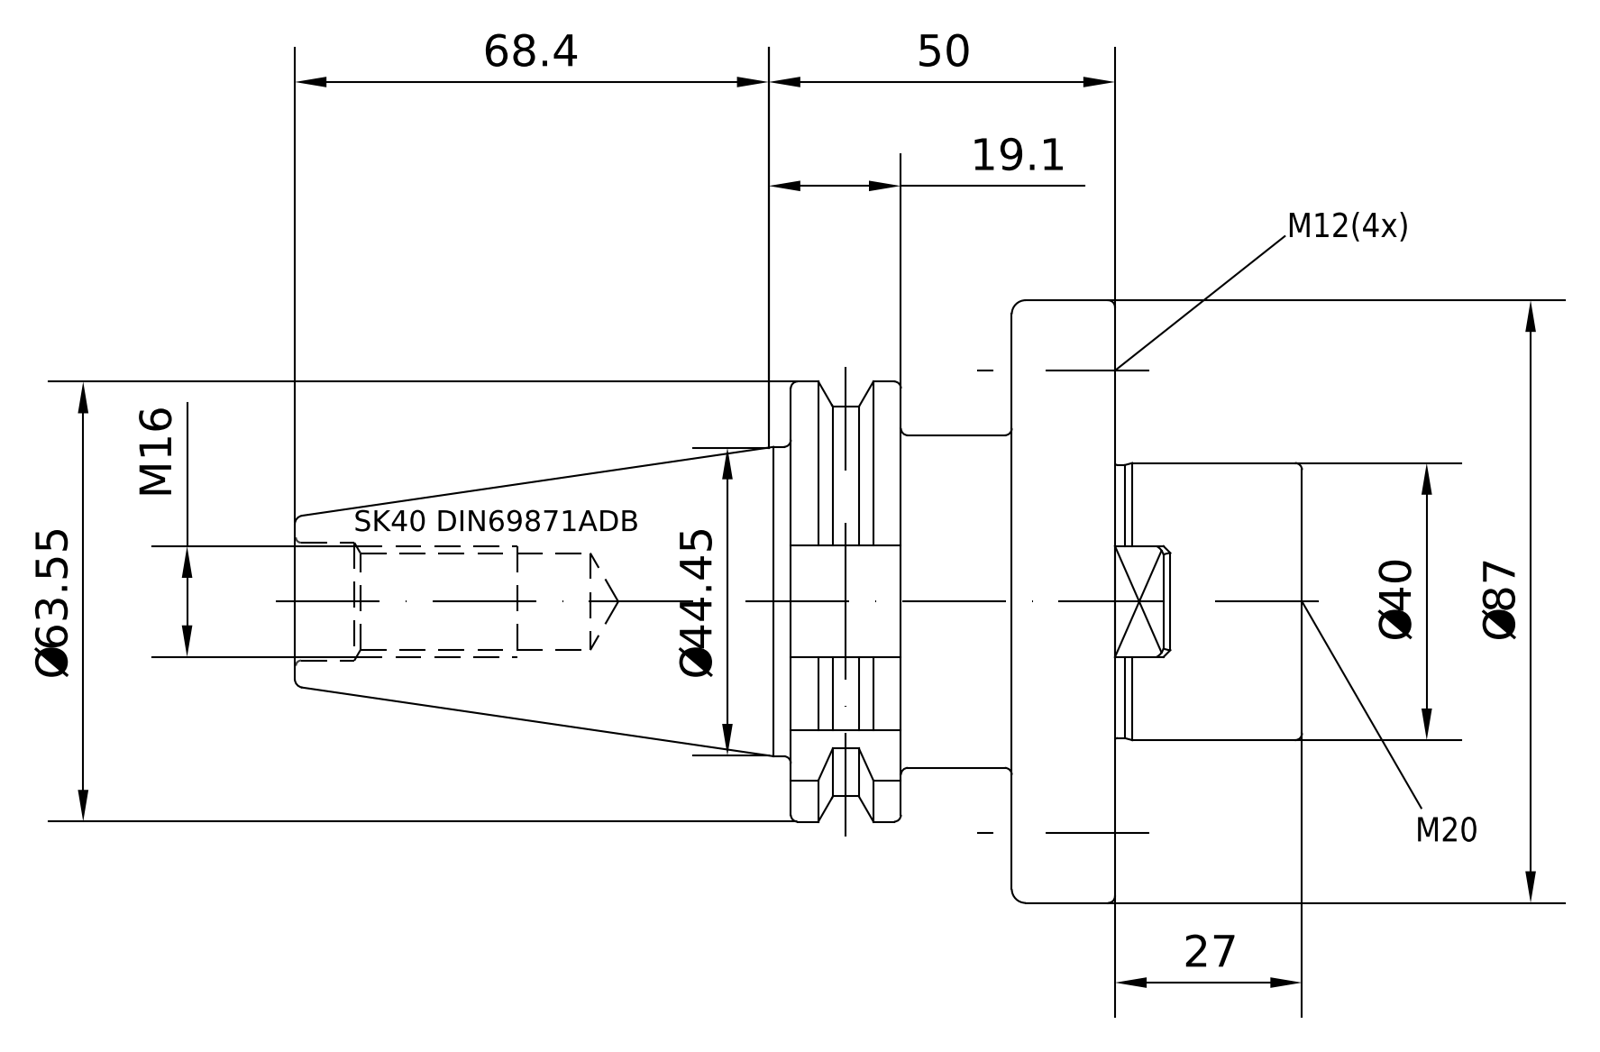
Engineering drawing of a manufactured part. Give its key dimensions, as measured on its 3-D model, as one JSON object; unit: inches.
{"part_name": "40-350-40", "step_written_by": "PRO/ENGINEER BY PARAMETRIC TECHNOLOGY CORPORATION, 2010430 (CONFIG_CONTROL_DESIGN)", "units": "inches", "bodies": {"solids": 1, "faces": 139, "planar": 38, "cylindrical": 49, "other": 52}, "overall_size": [5.719, 3.425, 3.425], "volume_in3": 14.96, "surface_area_in2": 73.02, "round_holes": [[0.402, 4], [0.472, 4], [0.545, 1], [0.67, 1], [0.689, 1], [0.787, 1]], "round_bosses_or_shafts": [[3.425, 1], [1.89, 1], [1.722, 1], [1.575, 1], [0.63, 1]], "partial_cylinders_radius": [[0.053, 5], [1.102, 1], [1.25, 1]], "face_to_face_distances": [0.589, 0.63, 1.254, 1.843, 2.906, 1.652, 1.063, 0.624, 1.219, 2.281], "hole_center_spacings": [1.313, 1.857, 2.626]}
